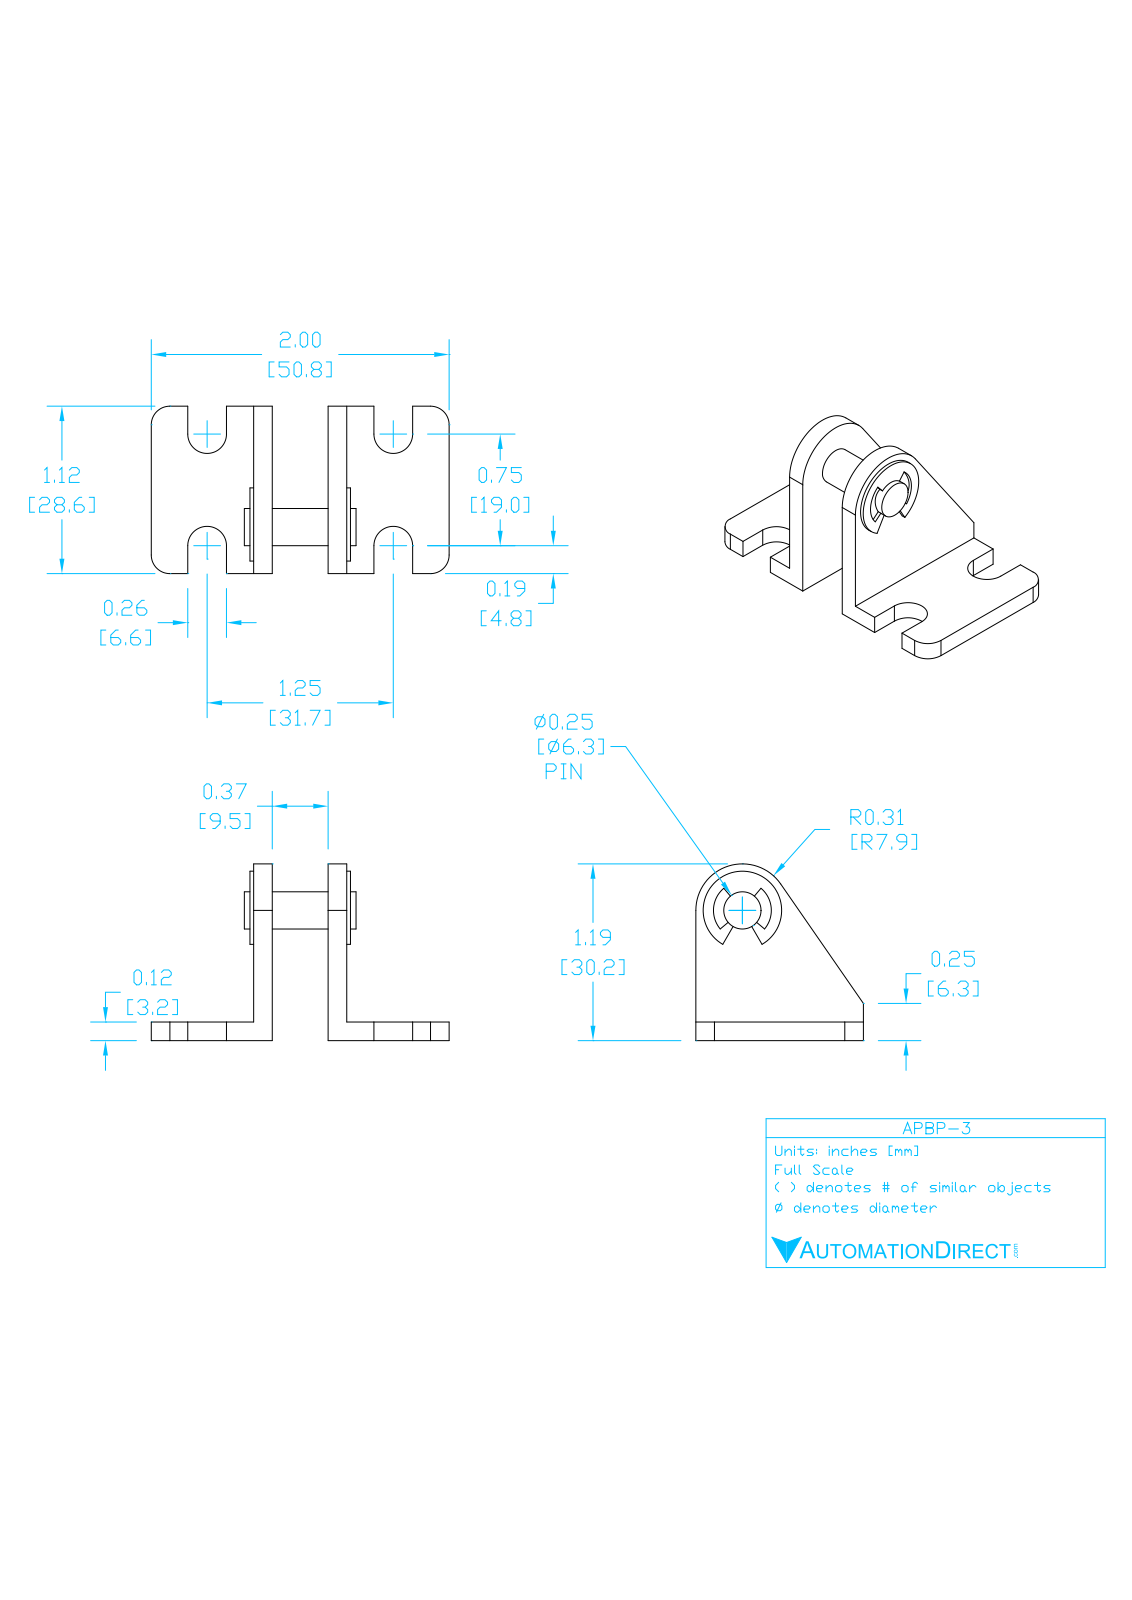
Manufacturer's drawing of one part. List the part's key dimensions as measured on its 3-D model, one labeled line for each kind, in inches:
Part name (STEP PRODUCT): APBP-3
STEP written by: SolidWorks 2017 (AUTOMOTIVE_DESIGN)
Units: inches
Bodies: 3 solids, 58 faces (38 planar, 20 cylindrical, 0 other)
Overall size (bounding box): 1.992 × 1.189 × 1.126
Volume: 0.422 in³ · Surface area: 8.573 in²
Round holes (diameter × count): ⌀0.248 ×1
Round bosses / shafts (diameter × count): ⌀0.25 ×1
Partial cylindrical surfaces — rounded edges, fillets, slot ends (radius × count): R0.125 ×4, R0.13 ×4, R0.03 ×2, R0.156 ×2, R0.311 ×1
Main face-to-face distances: 0.126, 0.496, 0.37, 0.622, 0.685, 0.811, 1.181, 1.307, 1.126, 1.992
